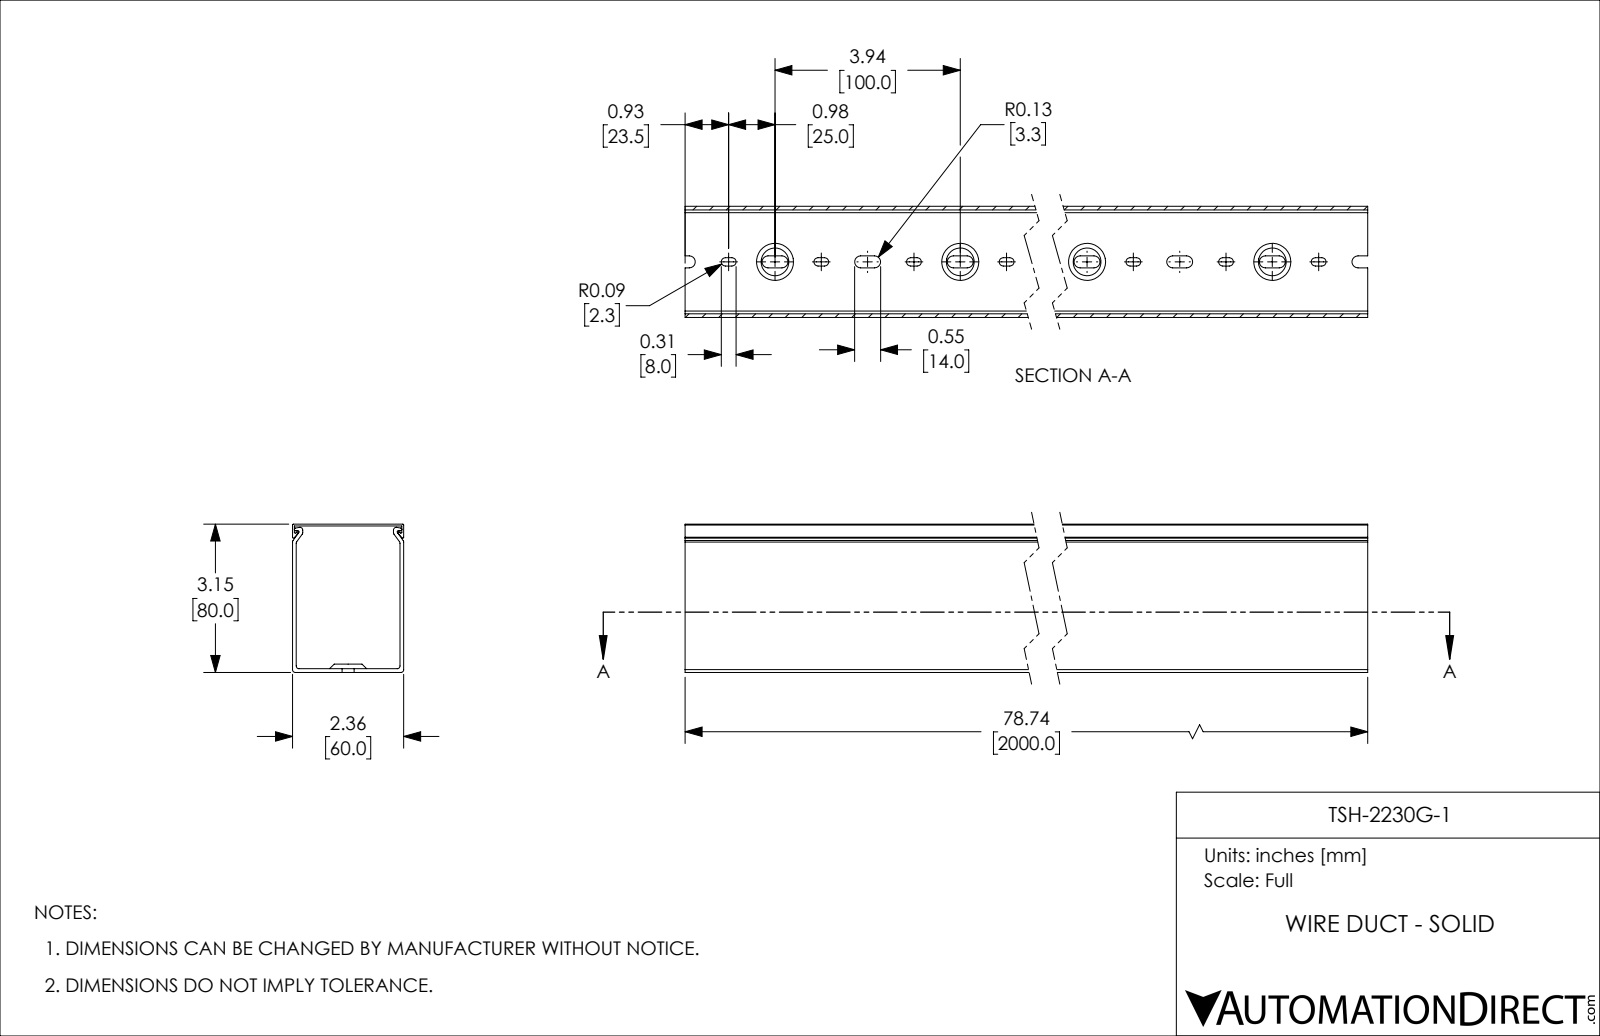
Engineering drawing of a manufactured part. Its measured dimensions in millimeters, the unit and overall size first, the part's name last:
Units: millimetres
Overall size (bounding box): 2000 × 80 × 60
Partial cylindrical surfaces — rounded edges, fillets, slot ends (radius × count): R2.25 ×80, R3.25 ×80, R1.5 ×12, R0.5 ×8, R0.75 ×6
Main face-to-face distances: 2, 58, 60, 1, 56, 79, 80, 77, 78, 59
Volume: 1 030 000 mm³ · Surface area: 1 182 000 mm²
Bodies: 2 solids, 525 faces (214 planar, 271 cylindrical, 40 other)
Part name (STEP PRODUCT): TSH-2230G-1
STEP written by: SolidWorks 2021 (CONFIG_CONTROL_DESIGN)
